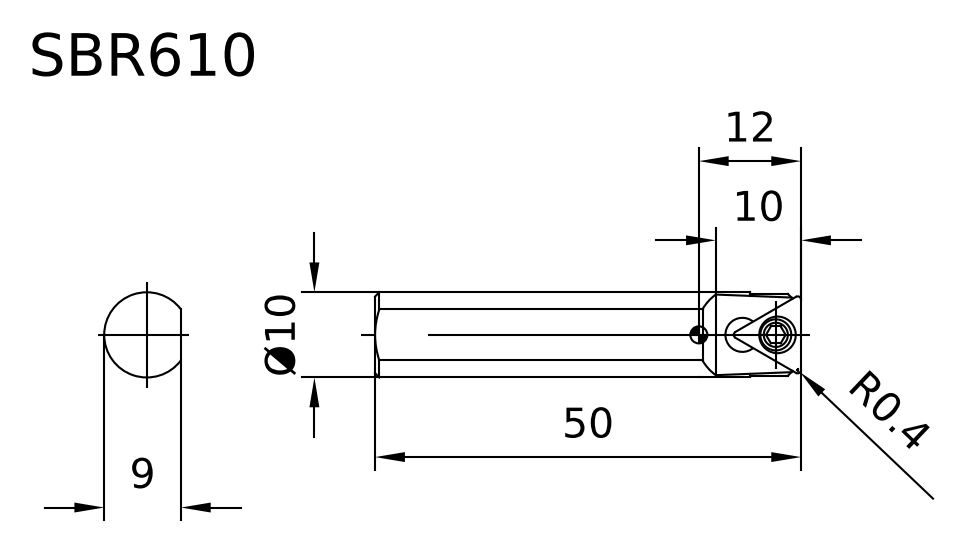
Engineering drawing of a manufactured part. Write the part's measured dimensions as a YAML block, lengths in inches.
part_name: "SBR610_ASM"
step_written_by: "SIEMENS PLM Software NX 10.0 (AUTOMOTIVE_DESIGN)"
units: inches
bodies: {solids: 2, faces: 64, planar: 20, cylindrical: 28, other: 16}
overall_size: [1.955, 0.394, 0.354]
volume: 0.21
surface_area: 2.745
round_holes:
  - {diameter: 0.039, count: 1}
  - {diameter: 0.098, count: 1}
round_bosses_or_shafts:
  - {diameter: 0.394, count: 1}
  - {diameter: 0.146, count: 1}
partial_cylinders:
  - {radius: 0.009, count: 6}
  - {radius: 0.019, count: 6}
  - {radius: 0.004, count: 4}
  - {radius: 0.02, count: 1}
  - {radius: 0.059, count: 1}
  - {radius: 0.189, count: 1}
face_to_face_distances: [0.082, 0.126, 0.207, 1.734, 0.118, 0.236, 0.111, 0.029, 0.22, 1.955]
